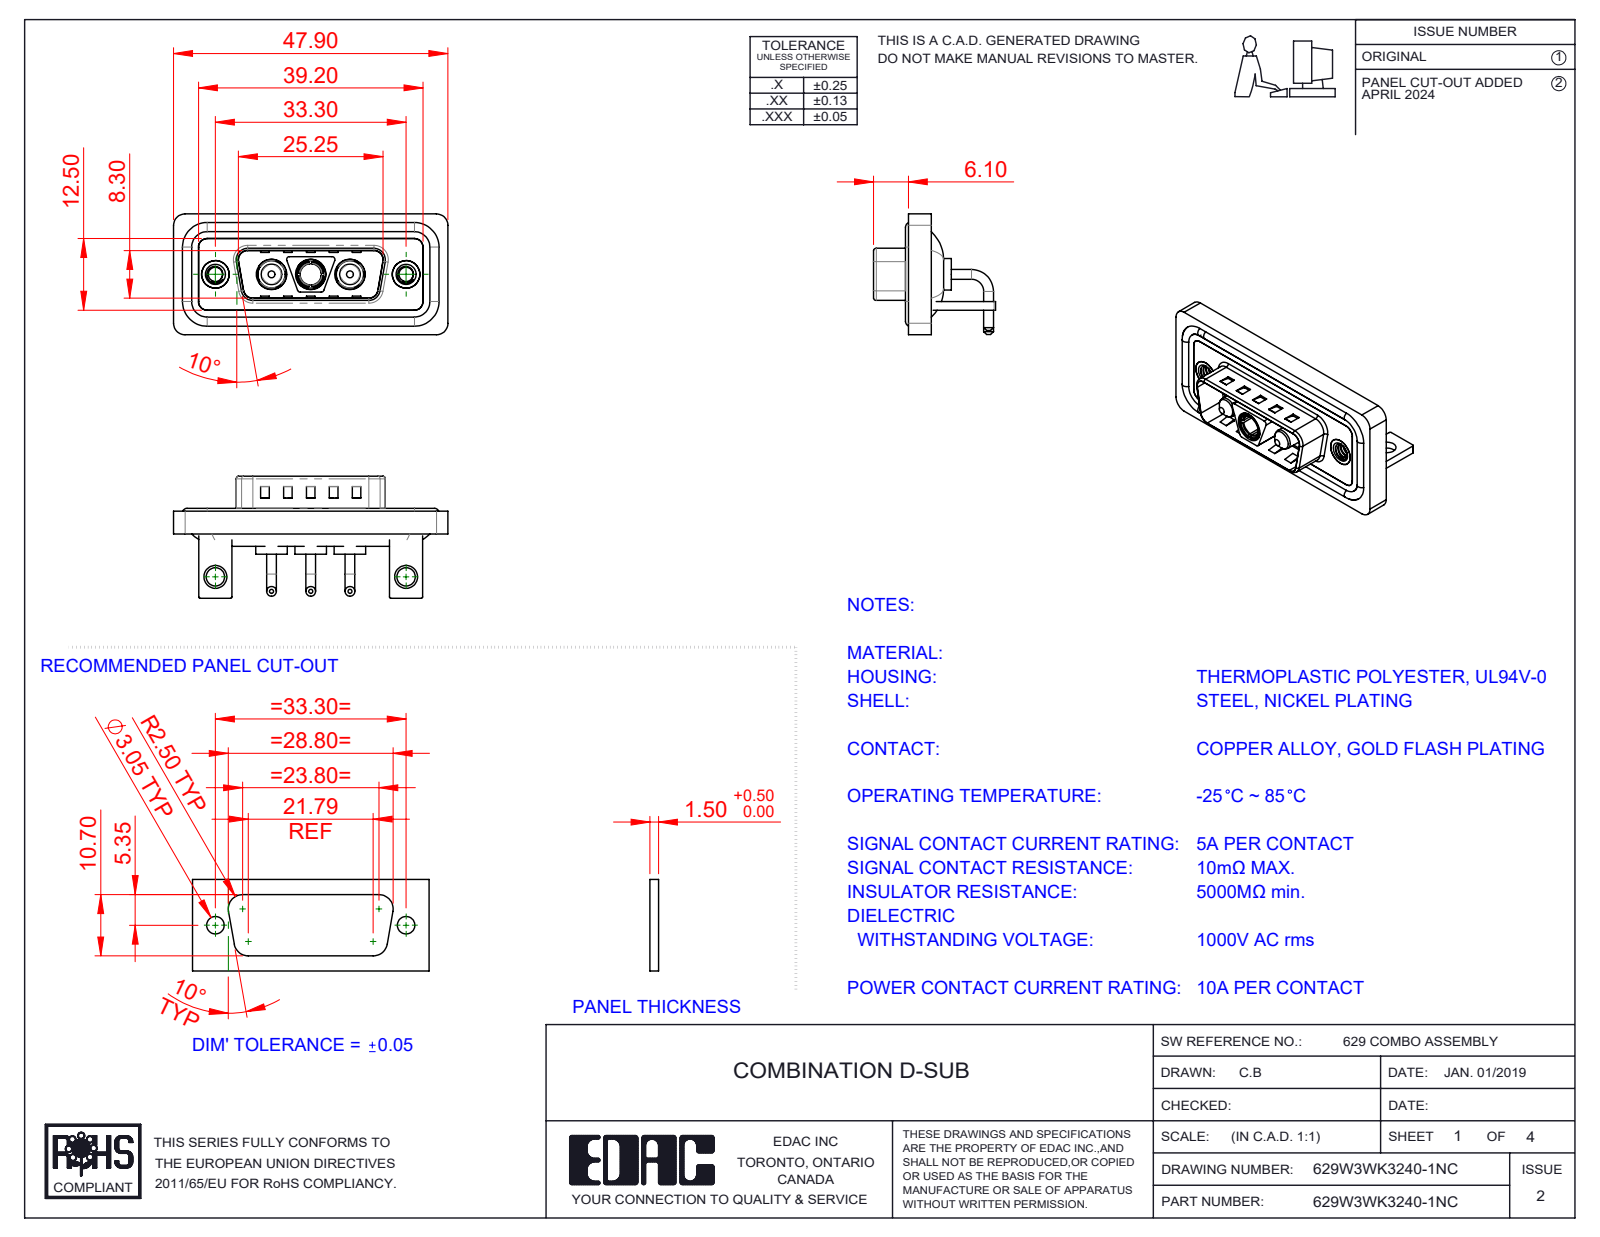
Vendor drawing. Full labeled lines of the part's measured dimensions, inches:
Part name (STEP PRODUCT): Power Socket_10A RA; 629Combo Waterproof Housing_15 Contacts; Power Pin_10A RA; 629Combo Shell Rear_15 Contacts (+5 more)
STEP written by: SolidWorks 2023 (CONFIG_CONTROL_DESIGN)
Units: inches
Bodies: 15 solids, 659 faces (251 planar, 274 cylindrical, 134 other)
Overall size (bounding box): 1.886 × 0.839 × 0.831
Volume: 0.365 in³ · Surface area: 15.27 in²
Round holes (diameter × count): ⌀0.191 ×3, ⌀0.209 ×3, ⌀0.098 ×2, ⌀0.126 ×2, ⌀0.157 ×2, ⌀0.189 ×2, ⌀0.197 ×2, ⌀0.146 ×1
Round bosses / shafts (diameter × count): ⌀0.067 ×6, ⌀0.063 ×4, ⌀0.217 ×3, ⌀0.205 ×3, ⌀0.187 ×3, ⌀0.148 ×3, ⌀0.193 ×2, ⌀0.142 ×2
Partial cylindrical surfaces — rounded edges, fillets, slot ends (radius × count): R0.079 ×21, R0.059 ×18, R0.01 ×16, R0.02 ×13, R0.063 ×8, R0.024 ×4, R0.026 ×4, R0.035 ×4
Main face-to-face distances: 0.016, 0.059, 0.031, 0.114, 0.043, 0.083, 0.146, 0.063, 0.047, 0.177
Hole centre spacings: 0.27, 0.386, 0.656, 0.925, 1.311, 0.539
